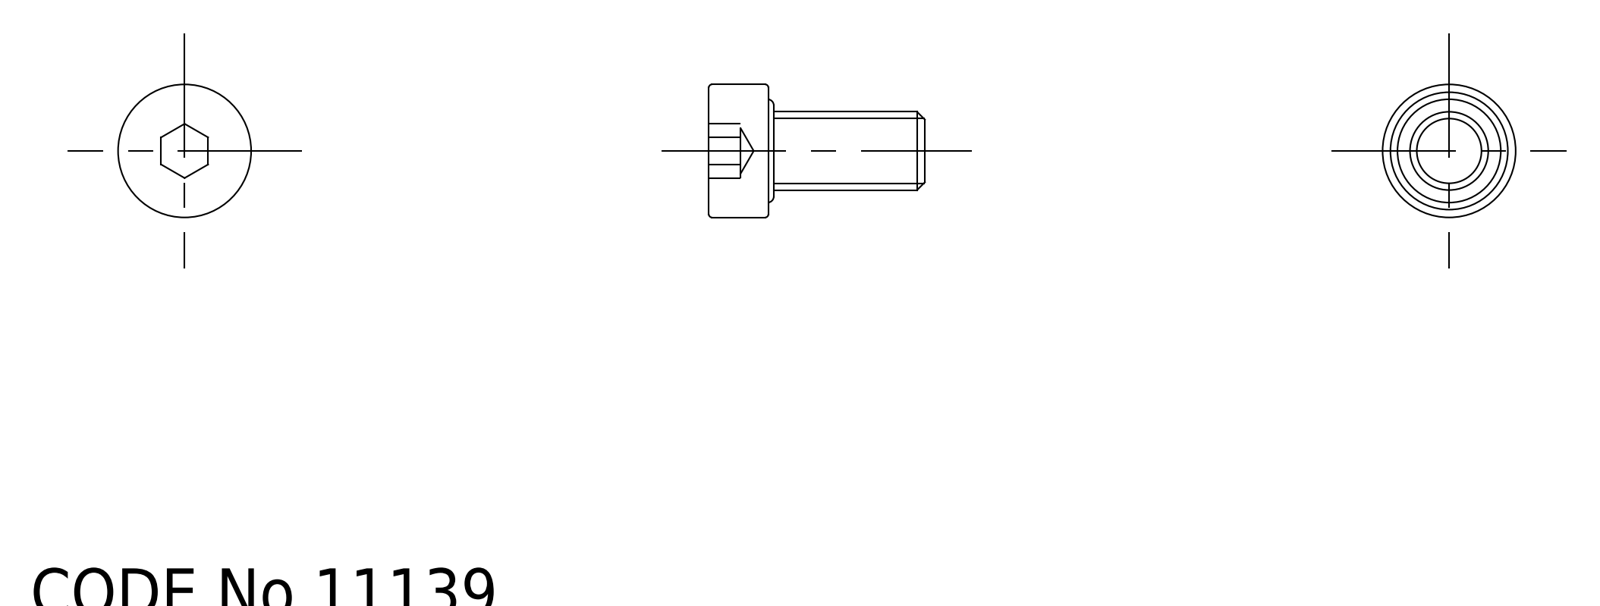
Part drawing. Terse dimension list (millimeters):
name: TL_418_M5_10; screw
written by: SolidWorks 2015 (AUTOMOTIVE_DESIGN)
unit: mm
bodies: 2 solids, 27 faces (11 planar, 6 cylindrical, 10 other)
size: 13.8 × 8.5 × 8.5
volume: 392 mm³; area: 447 mm²
holes: 1× ⌀7.5
bosses: 1× ⌀8.5, 1× ⌀5
face distances: 3.35, 13.8, 10.45, 3, 2, 1.35, 11.8, 3.8, 1.8, 0.45
